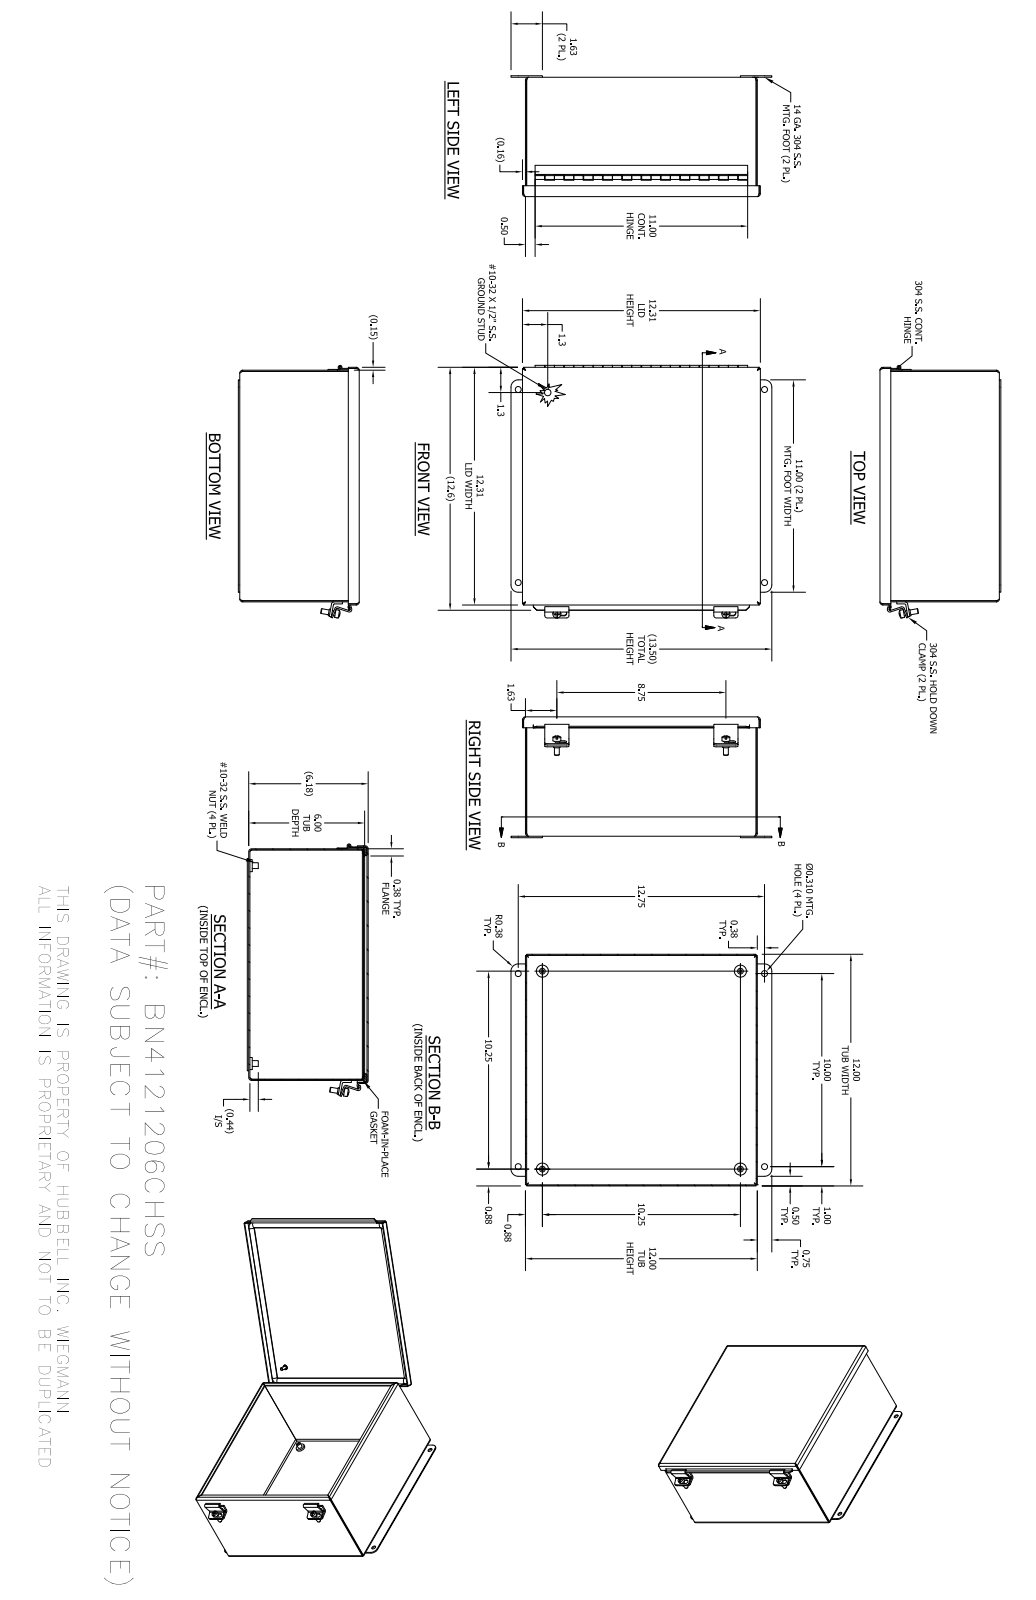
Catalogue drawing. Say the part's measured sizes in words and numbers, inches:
The part is named "B_121206_SSBKP; H4050551LH; H4050551P; H4050551TH (+8 more)". Its 3-D file was written by "Autodesk Inventor 2016 (AUTOMOTIVE_DESIGN)". It is 19 solids with 468 faces: 256 planar, 145 cylindrical and 67 other. Overall it measures 13.5 by 13.086 by 6.256 inches. Its volume is 44.53 cubic inches and its surface area 1 428 square inches. Round holes: 4 of diameter 0.11, 4 of diameter 0.156, 4 of diameter 0.31, 2 of diameter 0.196, 1 of diameter 0.117. Round bosses or shafts: 4 of diameter 0.625, 4 of diameter 0.3, 2 of diameter 0.409, 2 of diameter 0.344, 2 of diameter 0.25, 1 of diameter 0.337, 1 of diameter 0.2, 1 of diameter 0.19. Partial cylindrical surfaces (rounded edges, fillets, slot ends): 13 of radius 0.094, 13 of radius 0.153, 8 of radius 0.066, 8 of radius 0.125, 4 of radius 0.133, 4 of radius 0.228, 4 of radius 0.375, 3 of radius 0.063. The main face-to-face distances are 0.059, 6.122, 11.941, 6.181, 6.063, 12, 11.882, 5.941, 0.181, 0.075. The hole center spacings are 1.256, 8.75, 10.202, 10.25, 11.5, 15.322, 0.75, 10.
